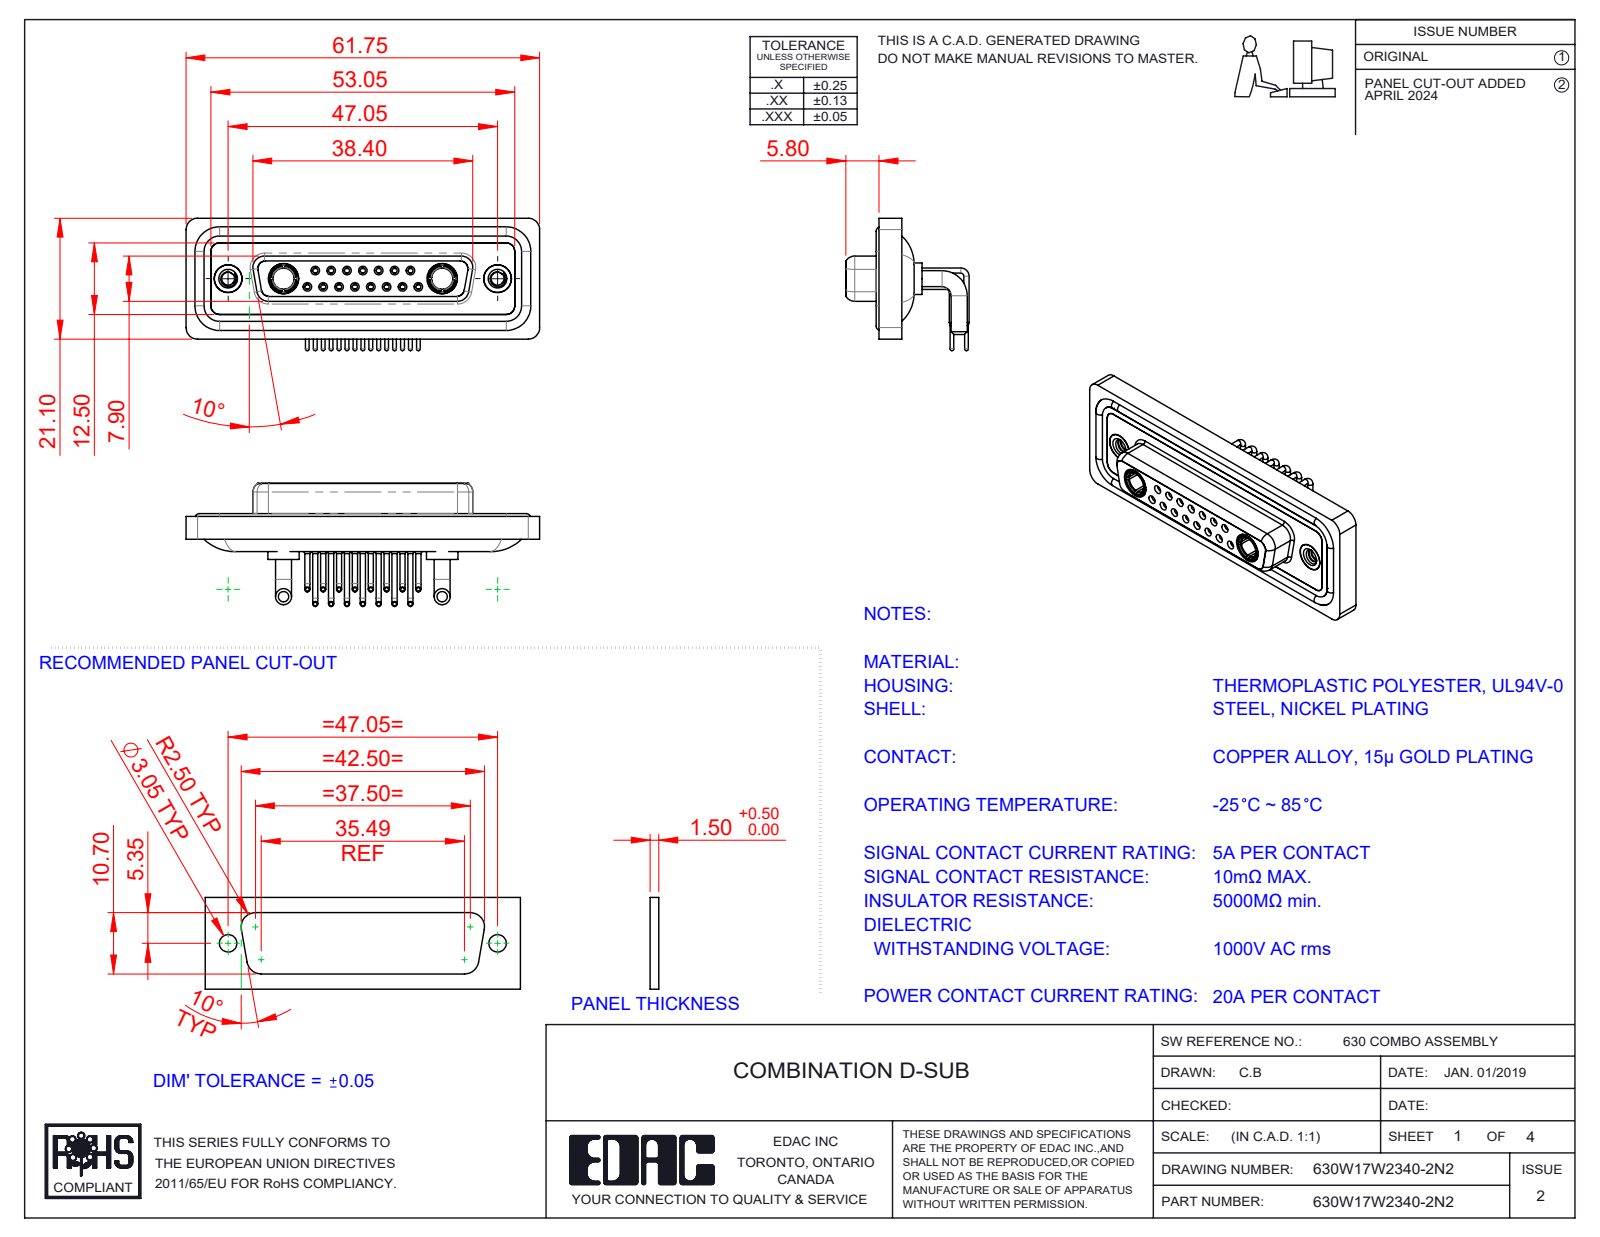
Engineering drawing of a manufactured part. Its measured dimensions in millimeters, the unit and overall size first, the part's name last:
Units: millimetres
Overall size (bounding box): 61.75 × 23.12 × 21.53
Round holes (diameter × count): ⌀0.9 ×15, ⌀1.1 ×15, ⌀1.5 ×15, ⌀2 ×15, ⌀1.6 ×8, ⌀1.7 ×7, ⌀4.85 ×4, ⌀2.26 ×2, ⌀3.7 ×2, ⌀4 ×2, ⌀4.05 ×2, ⌀5 ×2
Round bosses / shafts (diameter × count): ⌀0.9 ×15, ⌀0.65 ×15, ⌀1.6 ×11, ⌀2.8 ×4, ⌀5.5 ×2, ⌀5.2 ×2, ⌀4.96 ×2, ⌀4.95 ×2
Partial cylindrical surfaces — rounded edges, fillets, slot ends (radius × count): R1.5 ×18, R2 ×18, R1.35 ×8, R1.6 ×8, R0.25 ×4, R0.5 ×4, R0.6 ×4, R0.65 ×4
Main face-to-face distances: 0.4, 1.8, 4.1, 1.1, 1.6, 3.1, 2.5, 1.5, 3.7, 1.4
Hole centre spacings: 3.16, 2.77, 5.54, 8.31, 5.04, 7.49, 11.08, 5.03
Volume: 8 486 mm³ · Surface area: 14 530 mm²
Bodies: 26 solids, 1337 faces (388 planar, 583 cylindrical, 366 other)
Part name (STEP PRODUCT): 630Combo Contact Row 1_50 Contacts; 630Combo Housing_17W2; 630W17W2340-2N2; 630Combo Shell Front_25 Contacts (+5 more)
STEP written by: SolidWorks 2023 (CONFIG_CONTROL_DESIGN)
